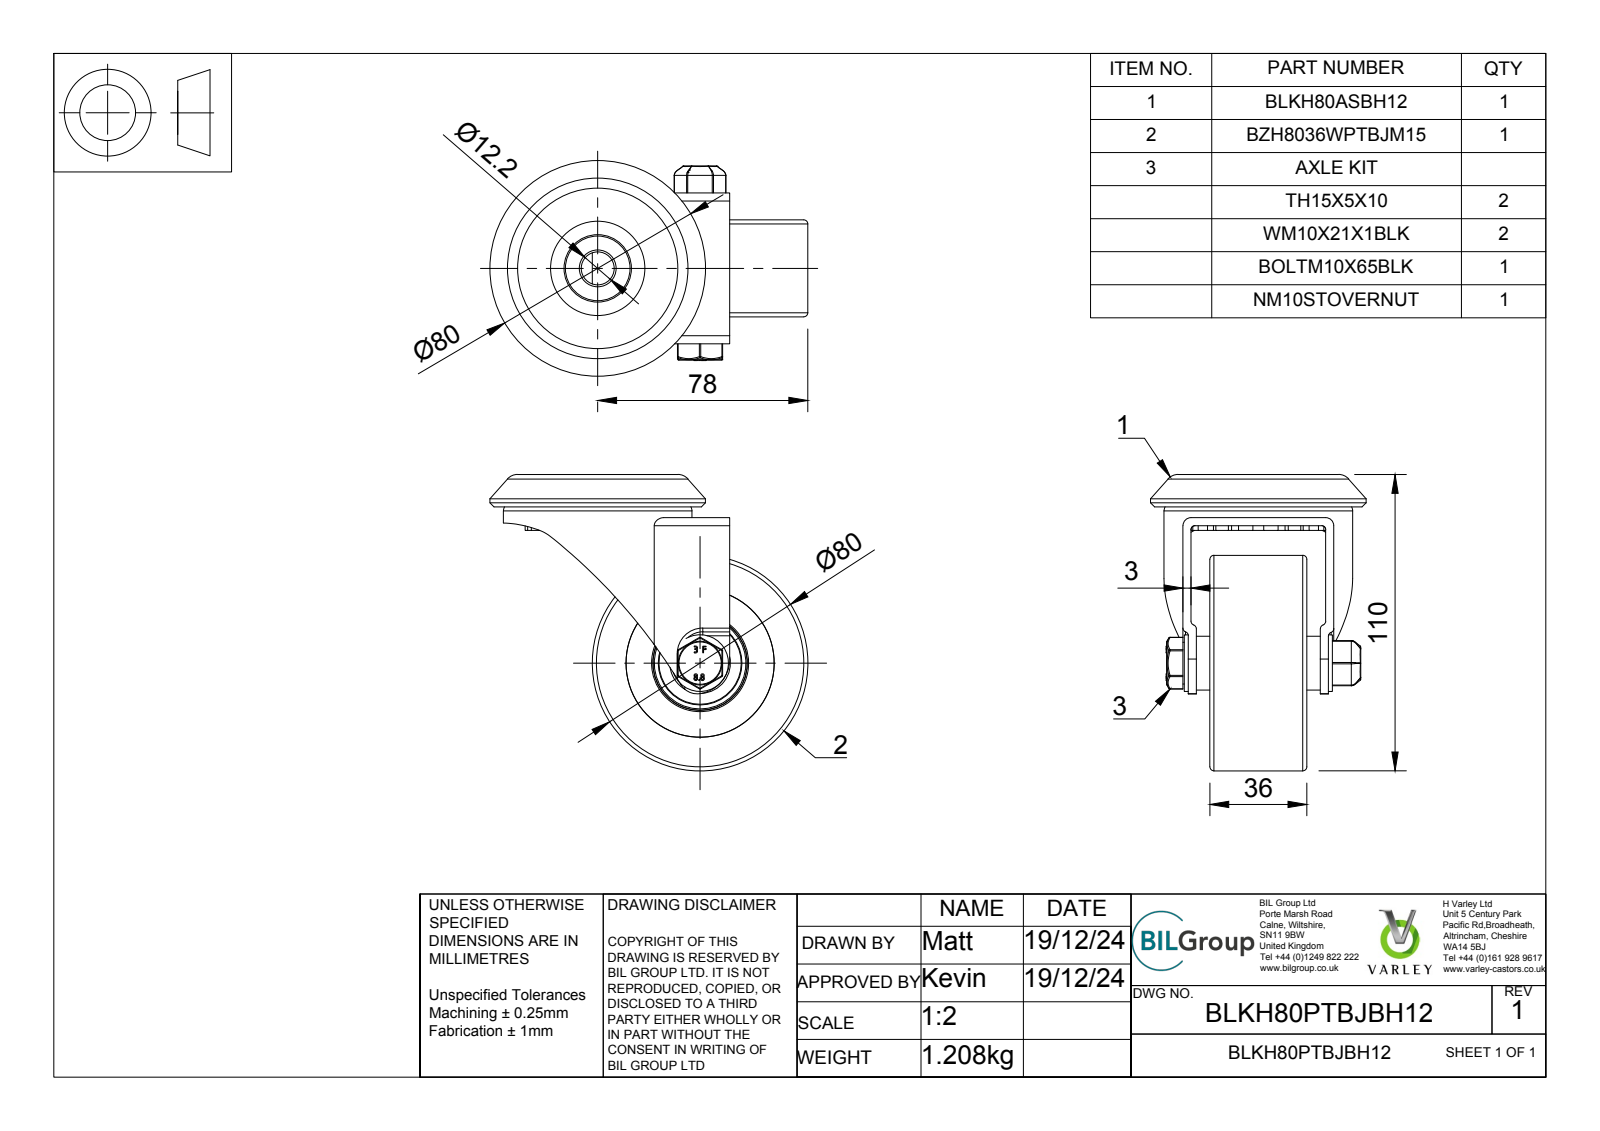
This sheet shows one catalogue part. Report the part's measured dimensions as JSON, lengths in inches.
{"part_name": "BLKH80PTBJBH12 v3; BLKH80ASBH12 v1; BLACK PAINTED TOP PLATE; BLACK PAINTED FORKS (+6 more)", "step_written_by": "Autodesk Translation Framework v13.20.0.188 (AP242_MANAGED_MODEL_BASED_3D_ENGINEERING_MIM_LF)", "units": "inches", "bodies": {"solids": 38, "faces": 1065, "planar": 434, "cylindrical": 214, "other": 417}, "overall_size": [4.646, 4.331, 3.15], "volume_in3": 13.92, "surface_area_in2": 164.5, "round_holes": [[0.394, 1], [0.413, 1], [0.48, 1], [0.591, 1], [0.886, 1], [0.984, 1], [1.102, 1], [1.181, 1], [1.22, 1], [1.26, 1], [1.378, 1], [2.165, 1]], "round_bosses_or_shafts": [[3.15, 2], [2.756, 1], [2.126, 1], [1.201, 1], [0.906, 1], [0.827, 1], [0.787, 1], [0.748, 1]], "partial_cylinders_radius": [[0.059, 14], [0.02, 12], [0.013, 4], [0.025, 4], [0.006, 3], [0.025, 3], [0.191, 3], [0.013, 2]], "face_to_face_distances": [0.118, 1.417, 0.404, 0.413, 0.059, 1.811, 0.6, 0.079, 0.394, 0.197]}
